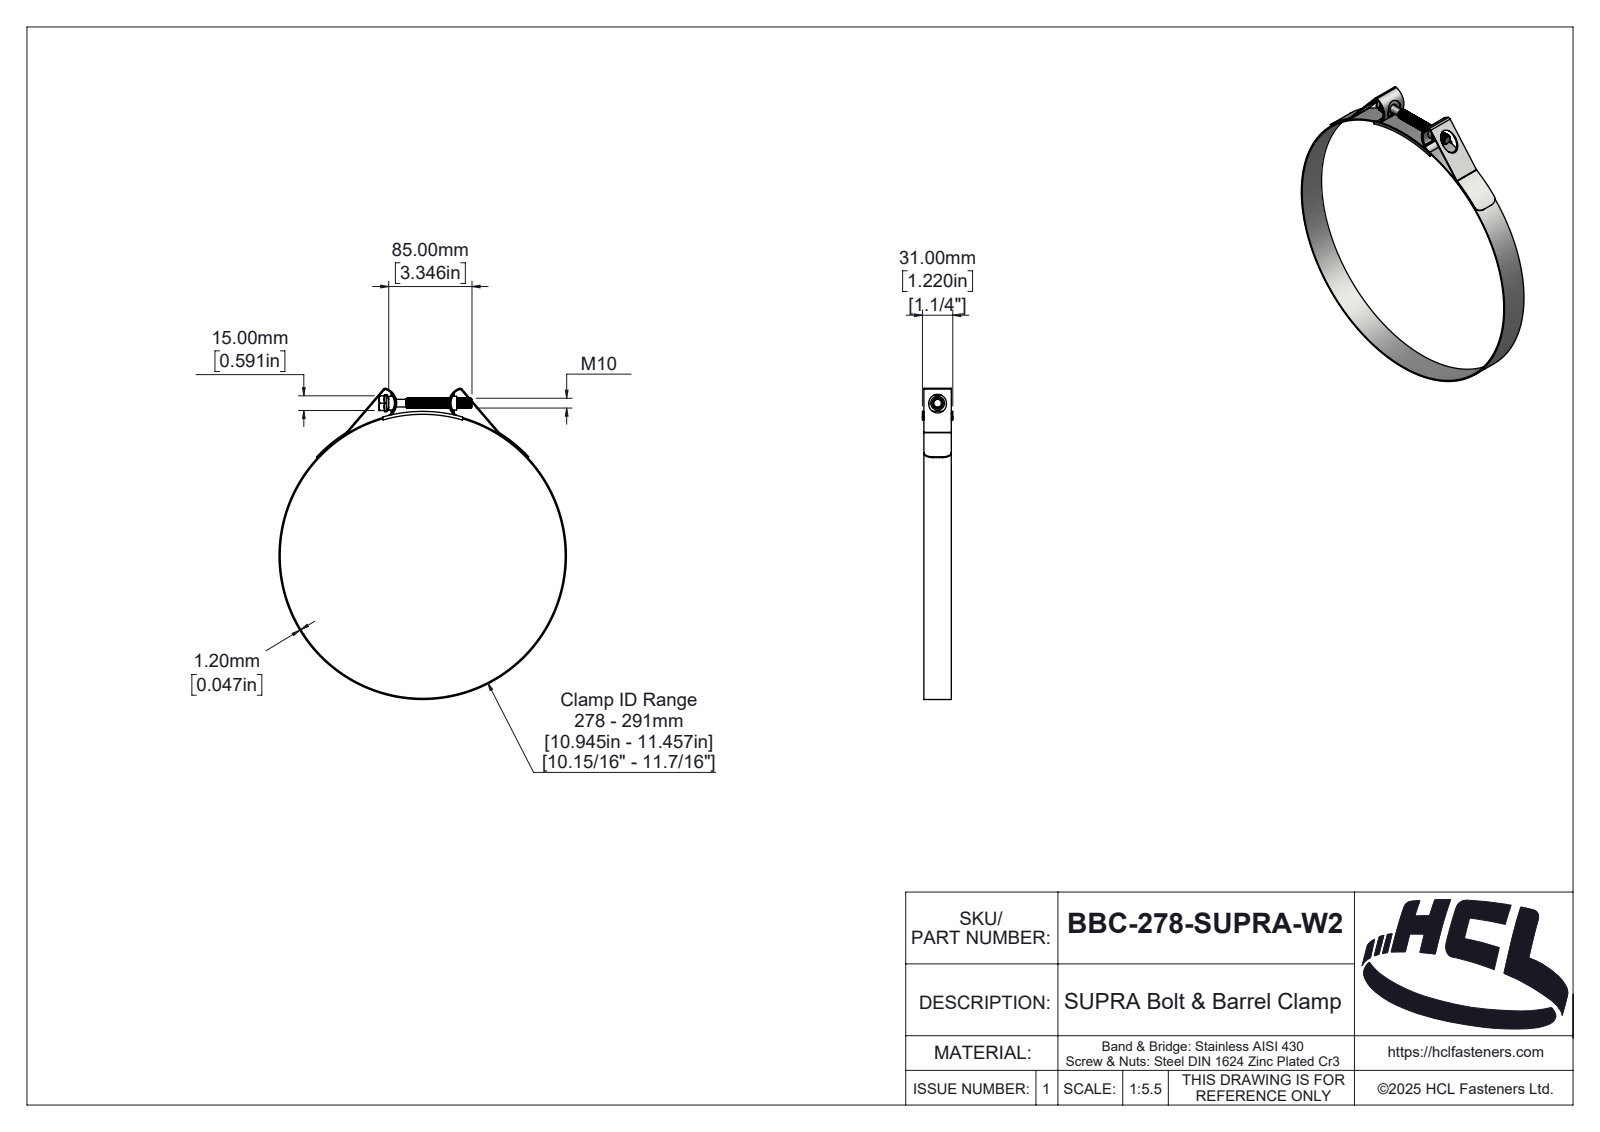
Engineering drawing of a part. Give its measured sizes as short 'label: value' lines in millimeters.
name: BBC-278-SUPRA-W2
written by: SolidWorks 2025 (AUTOMOTIVE_DESIGN)
unit: mm
bodies: 5 solids, 381 faces (50 planar, 244 cylindrical, 87 other)
size: 317.58 × 293.4 × 31
volume: 48 700 mm³; area: 76 643 mm²
holes: 1× ⌀291
bosses: 1× ⌀293.4, 1× ⌀17.32, 1× ⌀14, 1× ⌀10, 1× ⌀7.8
rounds: 4× R1, 2× R1.3, 2× R2, 2× R2.5, 2× R3.2, 2× R9, 2× R13.56, 2× R14.56
face distances: 1.2, 28, 1.5, 29.5, 29.8, 28.3, 31, 28.6, 15, 2.5
